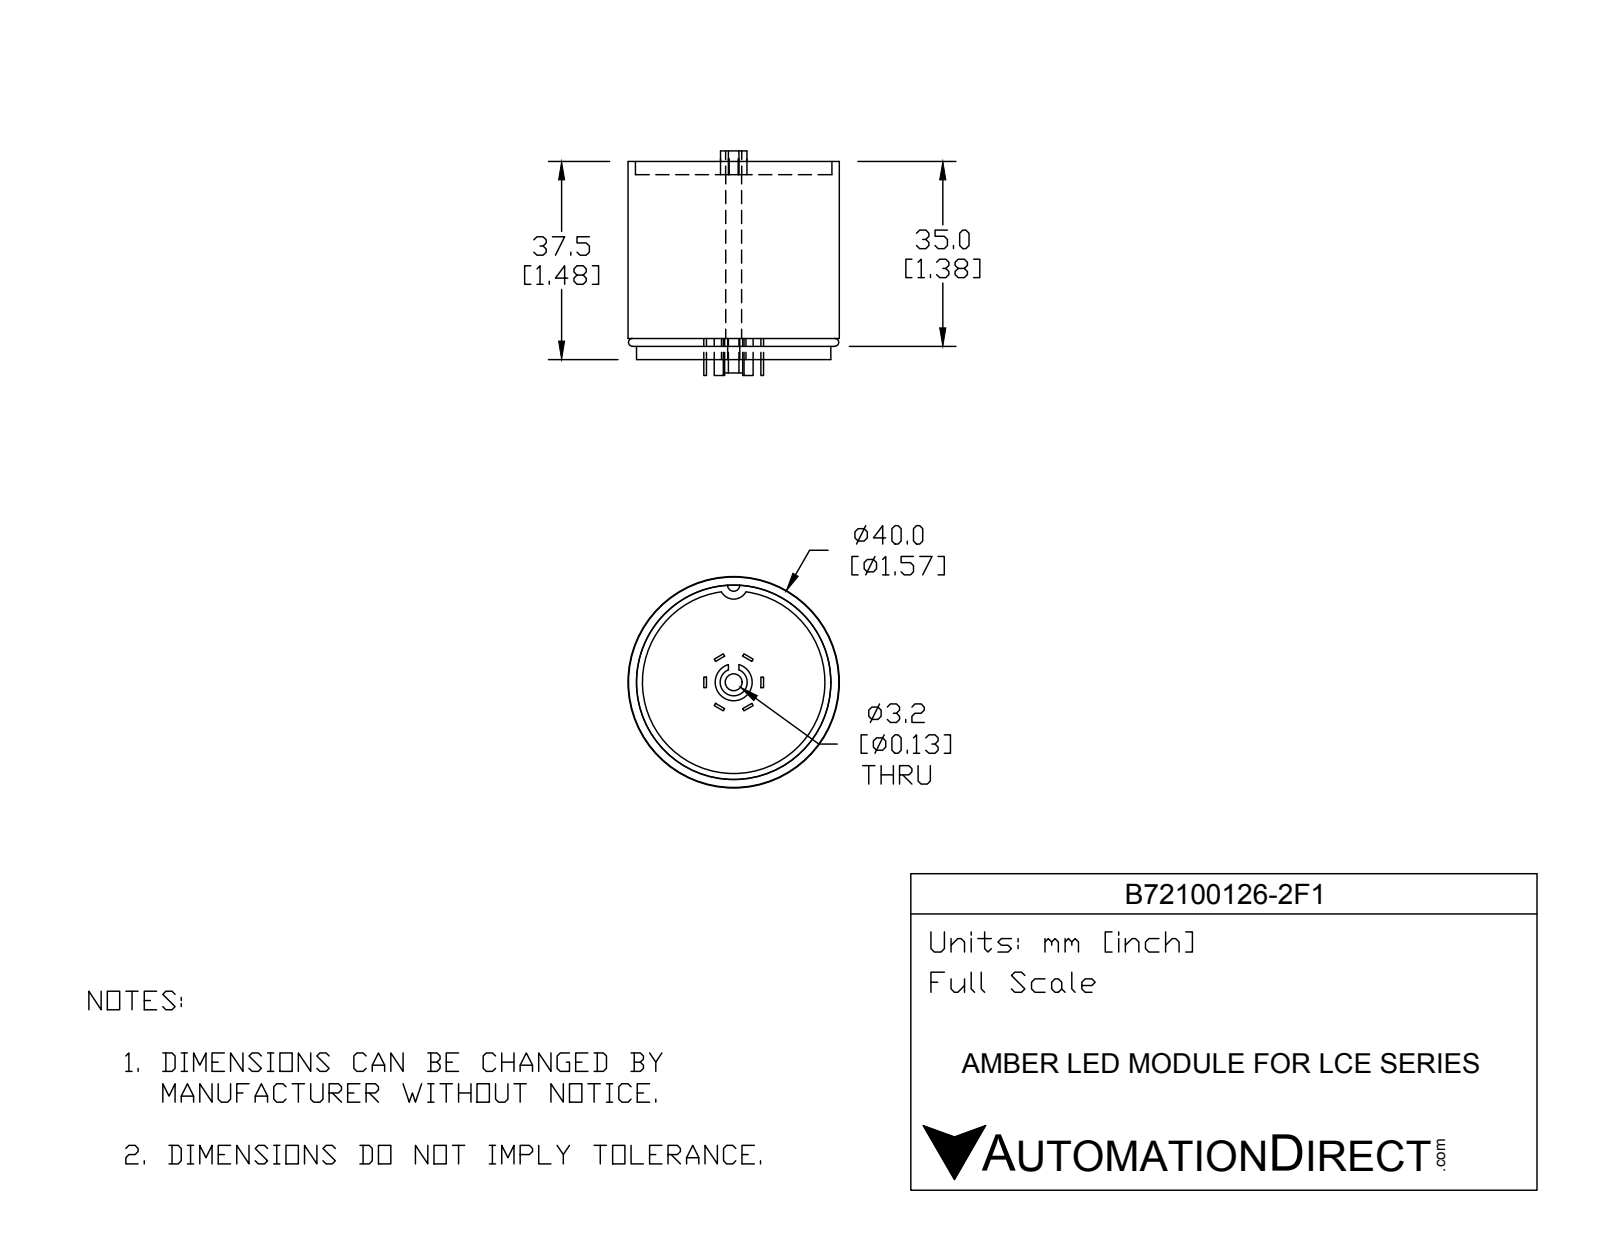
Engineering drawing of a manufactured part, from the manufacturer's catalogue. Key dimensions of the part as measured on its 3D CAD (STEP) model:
Part name (STEP PRODUCT): B72100126-2F1
STEP written by: SolidWorks 2016 (AUTOMOTIVE_DESIGN)
Units: millimetres
Bodies: 10 solids, 74 faces (50 planar, 20 cylindrical, 4 other)
Overall size (bounding box): 43.02 × 40 × 40
Volume: 40 201 mm³ · Surface area: 9 548 mm²
Round holes (diameter × count): ⌀3 ×1, ⌀3.06 ×1, ⌀5.1 ×1, ⌀34.54 ×1, ⌀37.2 ×1
Round bosses / shafts (diameter × count): ⌀40 ×1, ⌀36.8 ×1, ⌀7 ×1, ⌀5 ×1
Partial cylindrical surfaces — rounded edges, fillets, slot ends (radius × count): R0.9 ×1, R1.15 ×1, R2.65 ×1
Main face-to-face distances: 31, 34, 3, 4, 35, 38, 0.5, 10.8, 2, 11.3
